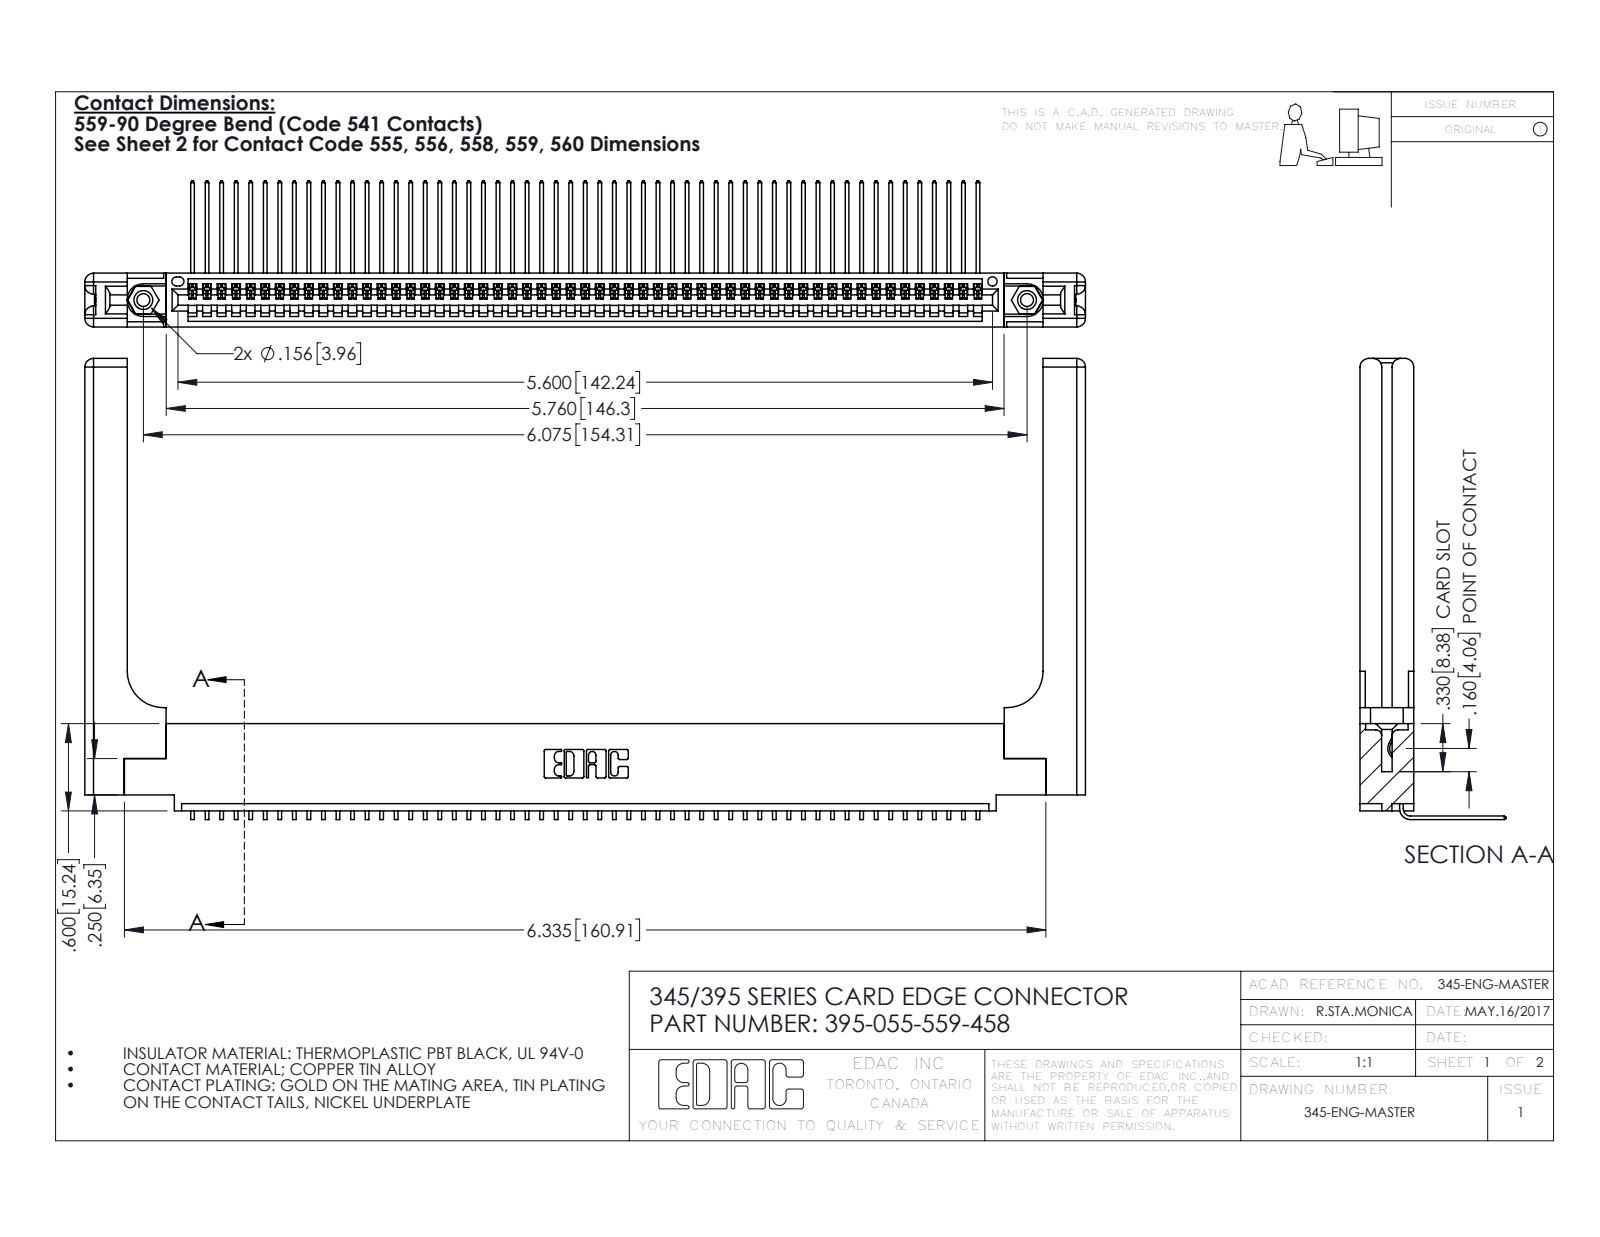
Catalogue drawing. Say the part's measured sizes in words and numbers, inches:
The part is named "395-055-559-458; 345-220-058_345-220-058; 345-250-001_345-250-001-102; 345 Part_0.110 Offset - 0.156 Dia-TH (+1 more)". Its 3-D file was written by "SolidWorks 2016 (CONFIG_CONTROL_DESIGN)". It is 60 solids with 3686 faces: 2542 planar, 1084 cylindrical and 60 other. Overall it measures 6.879 by 3.169 by 1.005 inches. Its volume is 1.545 cubic inches and its surface area 44.92 square inches. Round holes: 2 of diameter 0.089, 2 of diameter 0.125, 2 of diameter 0.156, 1 of diameter 0.064. Round bosses or shafts: 2 of diameter 0.155. Partial cylindrical surfaces (rounded edges, fillets, slot ends): 110 of radius 0.006, 22 of radius 0.01, 16 of radius 0.06, 6 of radius 0.007, 6 of radius 0.031, 3 of radius 0.026, 2 of radius 0.03, 2 of radius 0.031. The main face-to-face distances are 0.072, 0.37, 0.298, 0.098, 0.272, 0.025, 0.2, 0.225, 0.148, 0.15. The hole center spacings are 0.27, 5.839, 6.075.
